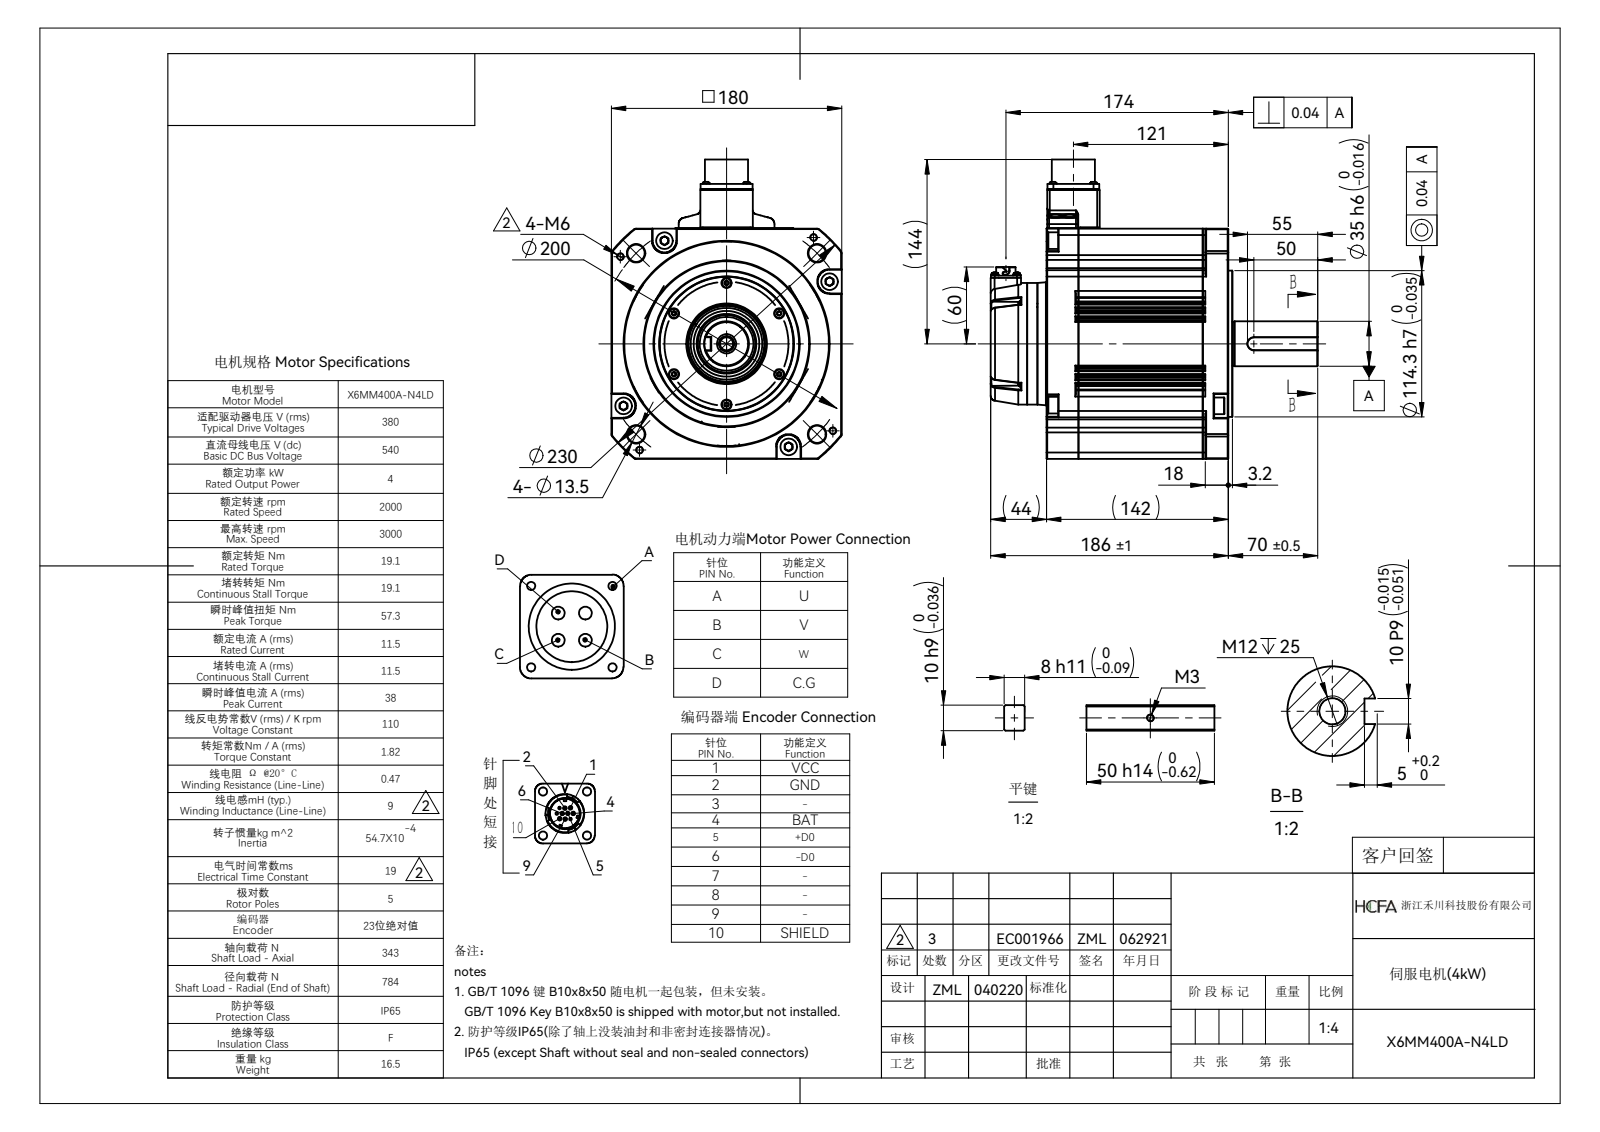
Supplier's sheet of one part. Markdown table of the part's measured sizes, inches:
| quantity | value |
| --- | --- |
| part name | SV-X6MM400A-N4LD |
| STEP written by | SolidWorks 2016 (CONFIG_CONTROL_DESIGN) |
| units | inches |
| bodies | 1 solid, 2537 faces (859 planar, 977 cylindrical, 701 other) |
| overall size | 10.063 × 9.209 × 7.087 |
| volume | 271.5 in³ |
| surface area | 350.8 in² |
| round holes (diameter × count) | 0.531 × 4, 0.402 × 1, 0.457 × 1, 0.465 × 1, 1.091 × 1 |
| round bosses / shafts (diameter × count) | 0.039 × 10, 0.512 × 6, 0.264 × 4, 0.236 × 4, 0.224 × 4, 0.217 × 4, 0.197 × 4, 0.118 × 4 |
| partial cylindrical surfaces (radius × count) | 0.02 × 78, 0.006 × 48, 0.039 × 40, 0.079 × 28, 0.008 × 26, 0.197 × 25, 0.012 × 16, 0.118 × 14 |
| main face-to-face distances | 7.087, 1.28, 5.807, 5.591, 5.717, 0.126, 4.528, 0.157, 1.717, 7.307 |
| hole center spacings | 3.937, 5.568, 7.874, 2.079 |
